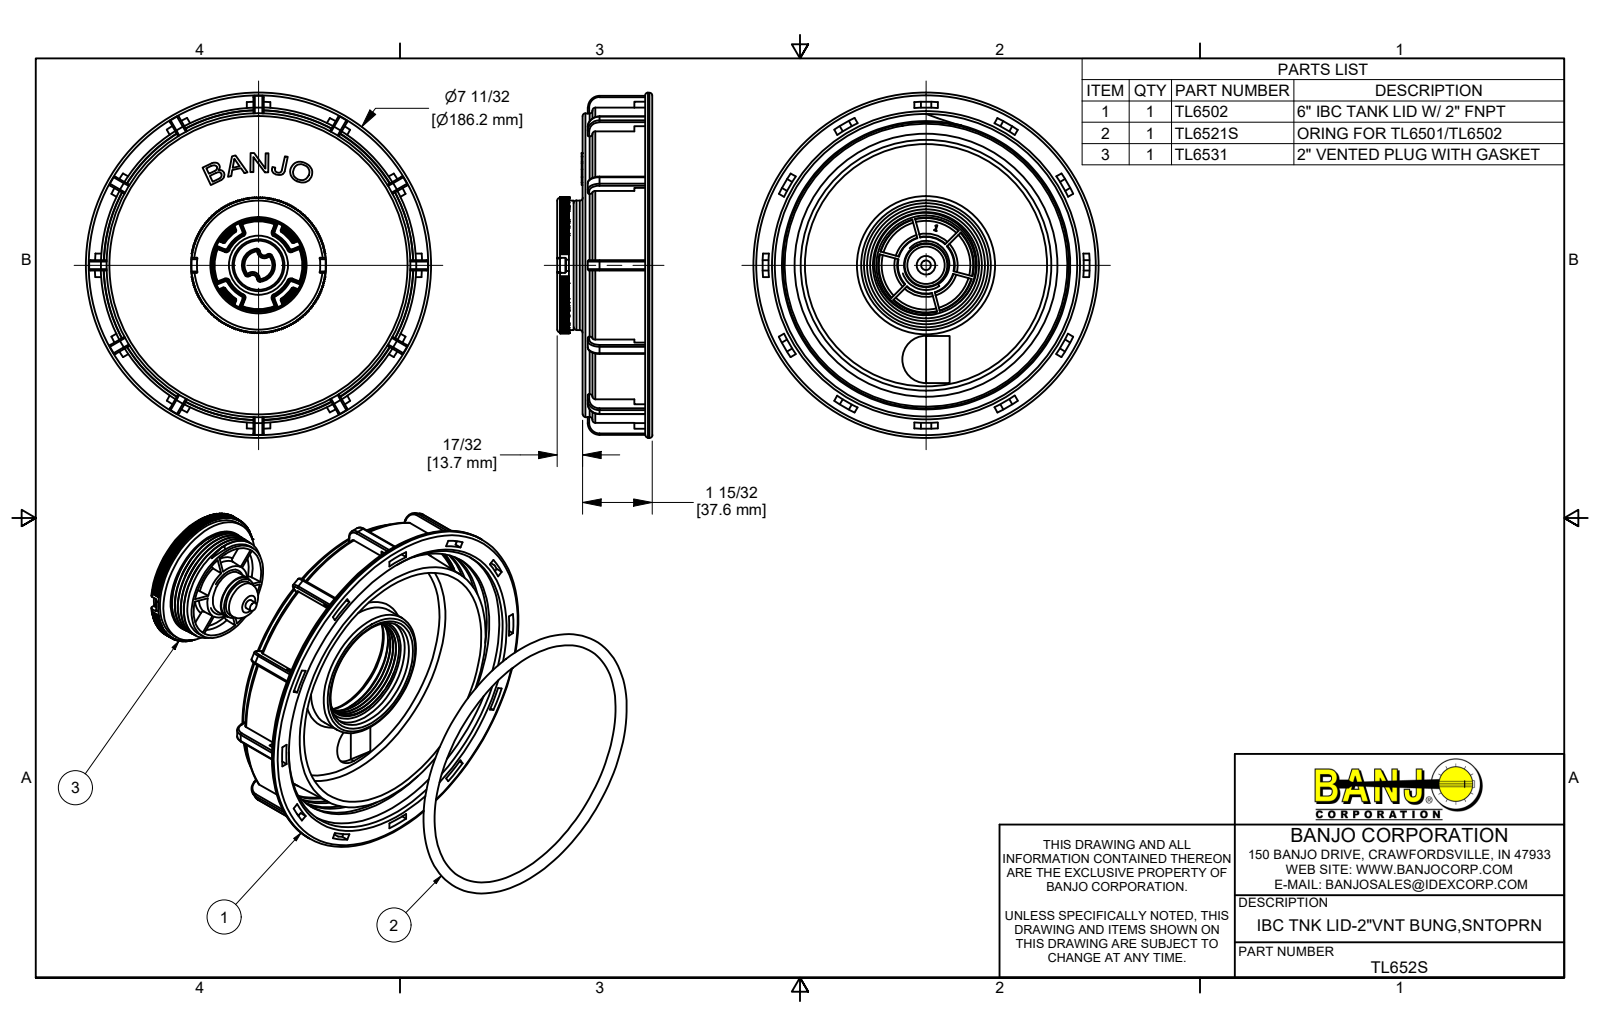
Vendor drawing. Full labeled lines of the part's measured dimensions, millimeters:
Part name (STEP PRODUCT): TL652S; TL6502; TL6521S; TL6531 (+3 more)
STEP written by: Autodesk Inventor 2022 (AUTOMOTIVE_DESIGN)
Units: millimetres
Bodies: 6 solids, 1695 faces (785 planar, 525 cylindrical, 385 other)
Overall size (bounding box): 186.2 × 186.2 × 51.3
Volume: 323 600 mm³ · Surface area: 166 500 mm²
Round holes (diameter × count): ⌀23.9 ×1, ⌀58.4 ×1, ⌀60.5 ×1, ⌀135.3 ×1, ⌀154.2 ×1, ⌀155.6 ×1, ⌀163.2 ×1
Round bosses / shafts (diameter × count): ⌀186.2 ×1, ⌀170.2 ×1, ⌀163.8 ×1, ⌀69.9 ×1, ⌀27.9 ×1, ⌀23.8 ×1, ⌀23 ×1, ⌀20.2 ×1
Partial cylindrical surfaces — rounded edges, fillets, slot ends (radius × count): R0.8 ×52, R0.4 ×36, R6.4 ×12, R3.2 ×2, R8 ×1, R8.3 ×1, R12.7 ×1, R15.3 ×1
Main face-to-face distances: 4.1, 37.6, 33.5, 8.9, 33.8, 29.7, 3.8, 6.4, 7.4, 11.4
